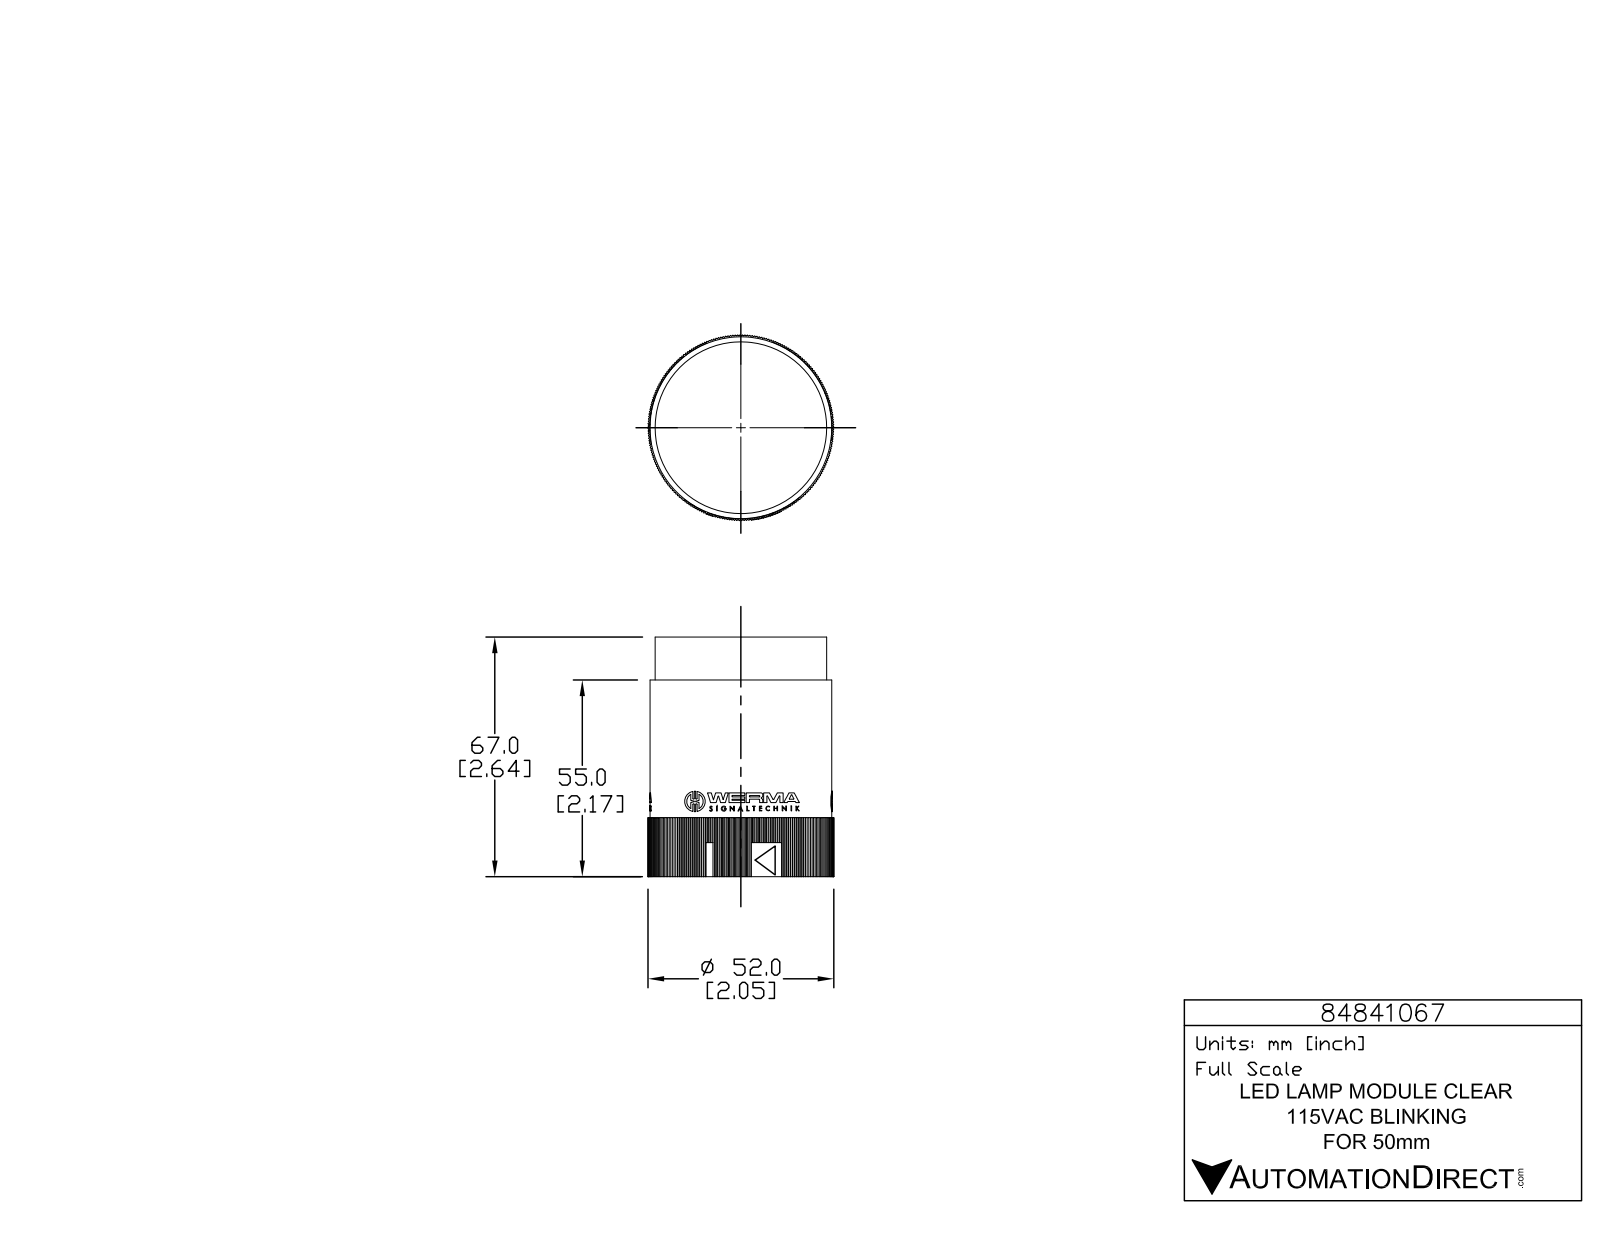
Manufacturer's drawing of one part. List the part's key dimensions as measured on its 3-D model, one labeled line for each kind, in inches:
Part name (STEP PRODUCT): 84841067
STEP written by: SolidWorks 2015 (AUTOMOTIVE_DESIGN)
Units: inches
Bodies: 1 solid, 1265 faces (1020 planar, 245 cylindrical, 0 other)
Overall size (bounding box): 2.638 × 2.047 × 2.047
Volume: 6.873 in³ · Surface area: 27.62 in²
Round holes (diameter × count): ⌀0.039 ×3, ⌀1.898 ×1
Round bosses / shafts (diameter × count): ⌀0.226 ×3, ⌀0.056 ×3, ⌀2.002 ×1, ⌀1.89 ×1
Partial cylindrical surfaces — rounded edges, fillets, slot ends (radius × count): R0.008 ×6, R0.008 ×6, R0.008 ×6, R0.131 ×6, R0.004 ×3, R0.005 ×3, R0.008 ×3, R0.008 ×3
Main face-to-face distances: 2.165, 1.428, 1.429, 1.429, 0.472, 2.638, 1.428, 1.428, 1.693, 1.988
